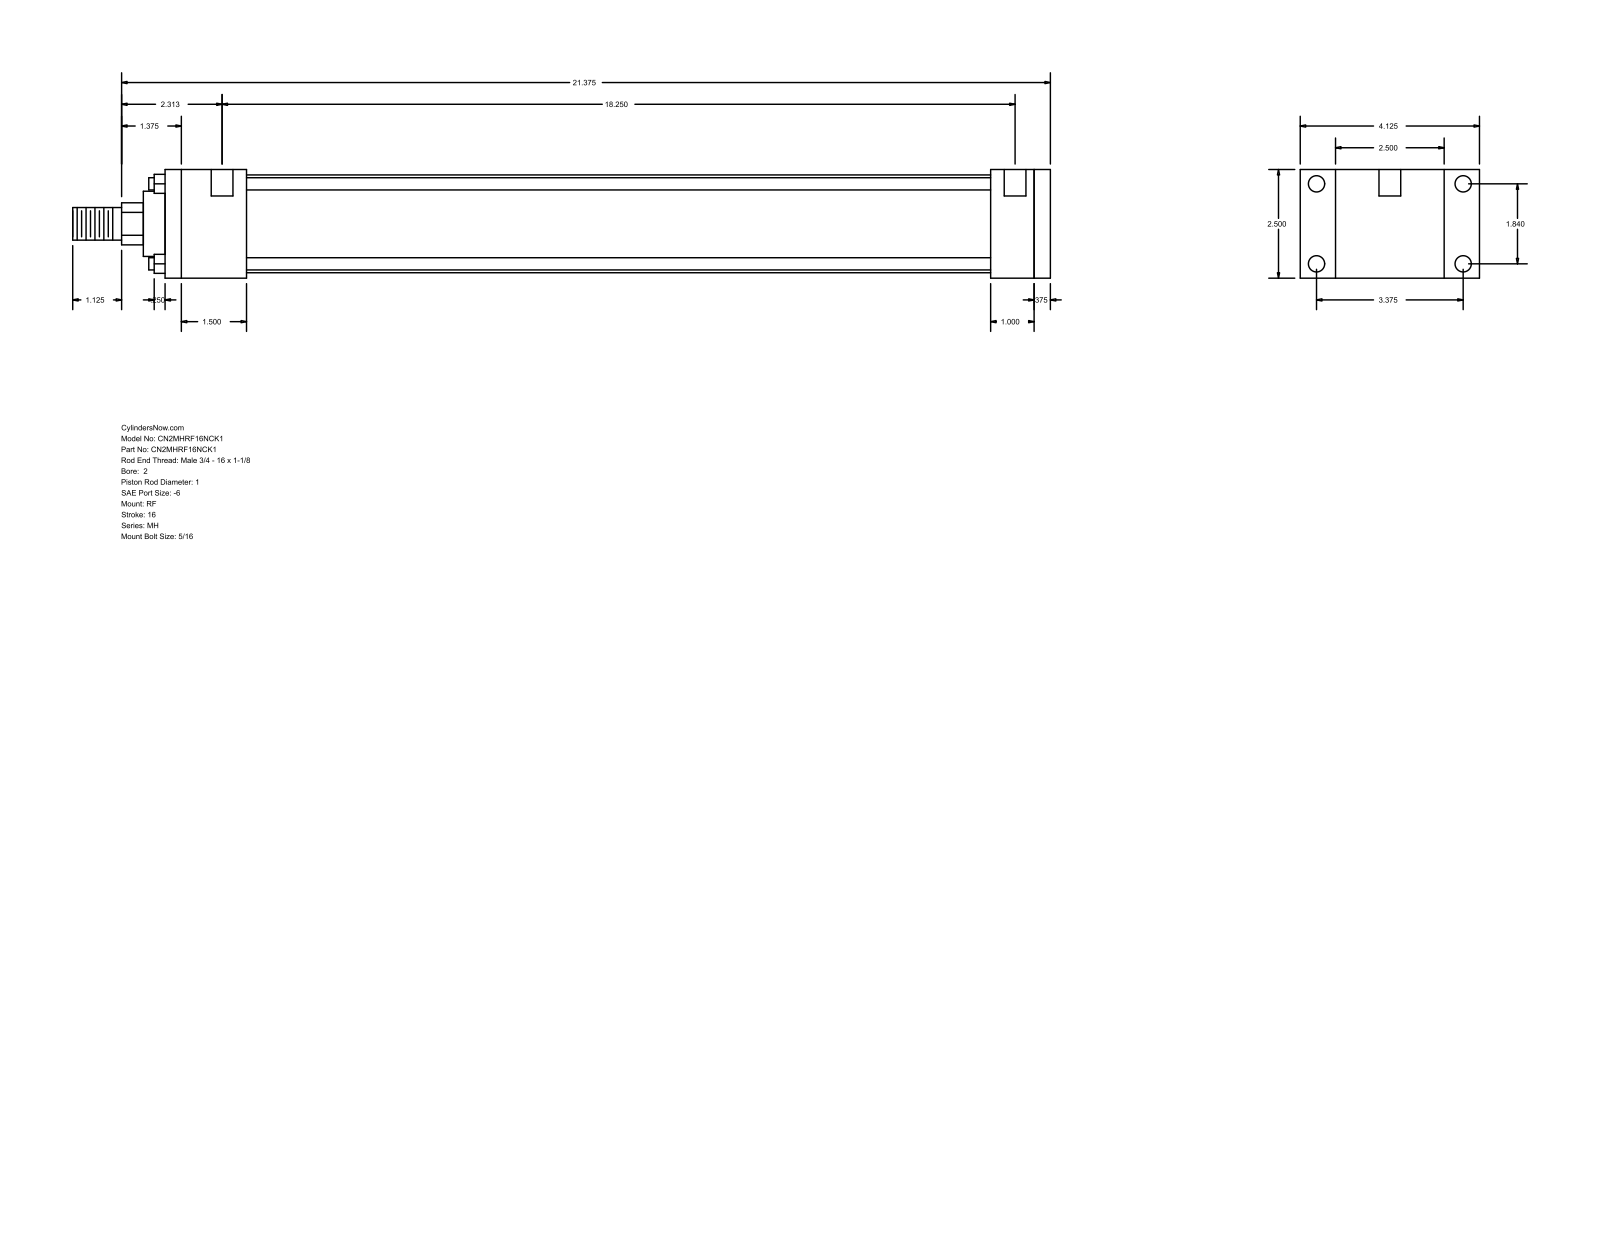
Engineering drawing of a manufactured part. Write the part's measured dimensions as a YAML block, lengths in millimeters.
part_name: "MH_RF__0200_1"
step_written_by: "GSSL Pune (CONFIG_CONTROL_DESIGN)"
units: millimeters
bodies: {solids: 0, faces: 92, planar: 64, cylindrical: 28, other: 0}
overall_size: [571.5, 104.78, 63.5]
round_holes:
  - {diameter: 5.56, count: 4}
  - {diameter: 9.53, count: 4}
  - {diameter: 12.7, count: 2}
round_bosses_or_shafts:
  - {diameter: 7.14, count: 4}
  - {diameter: 57.15, count: 1}
  - {diameter: 38.1, count: 1}
  - {diameter: 25.4, count: 1}
  - {diameter: 19.05, count: 1}
partial_cylinders:
  - {radius: 12.29, count: 1}
face_to_face_distances: [63.5, 517.52, 9.52, 508, 20.64, 25.4, 47.63, 482.6, 434.97, 460.37]
hole_center_spacings: [46.74, 85.72, 97.63, 471.48, 3.17, 4.76, 463.55, 466.72]
